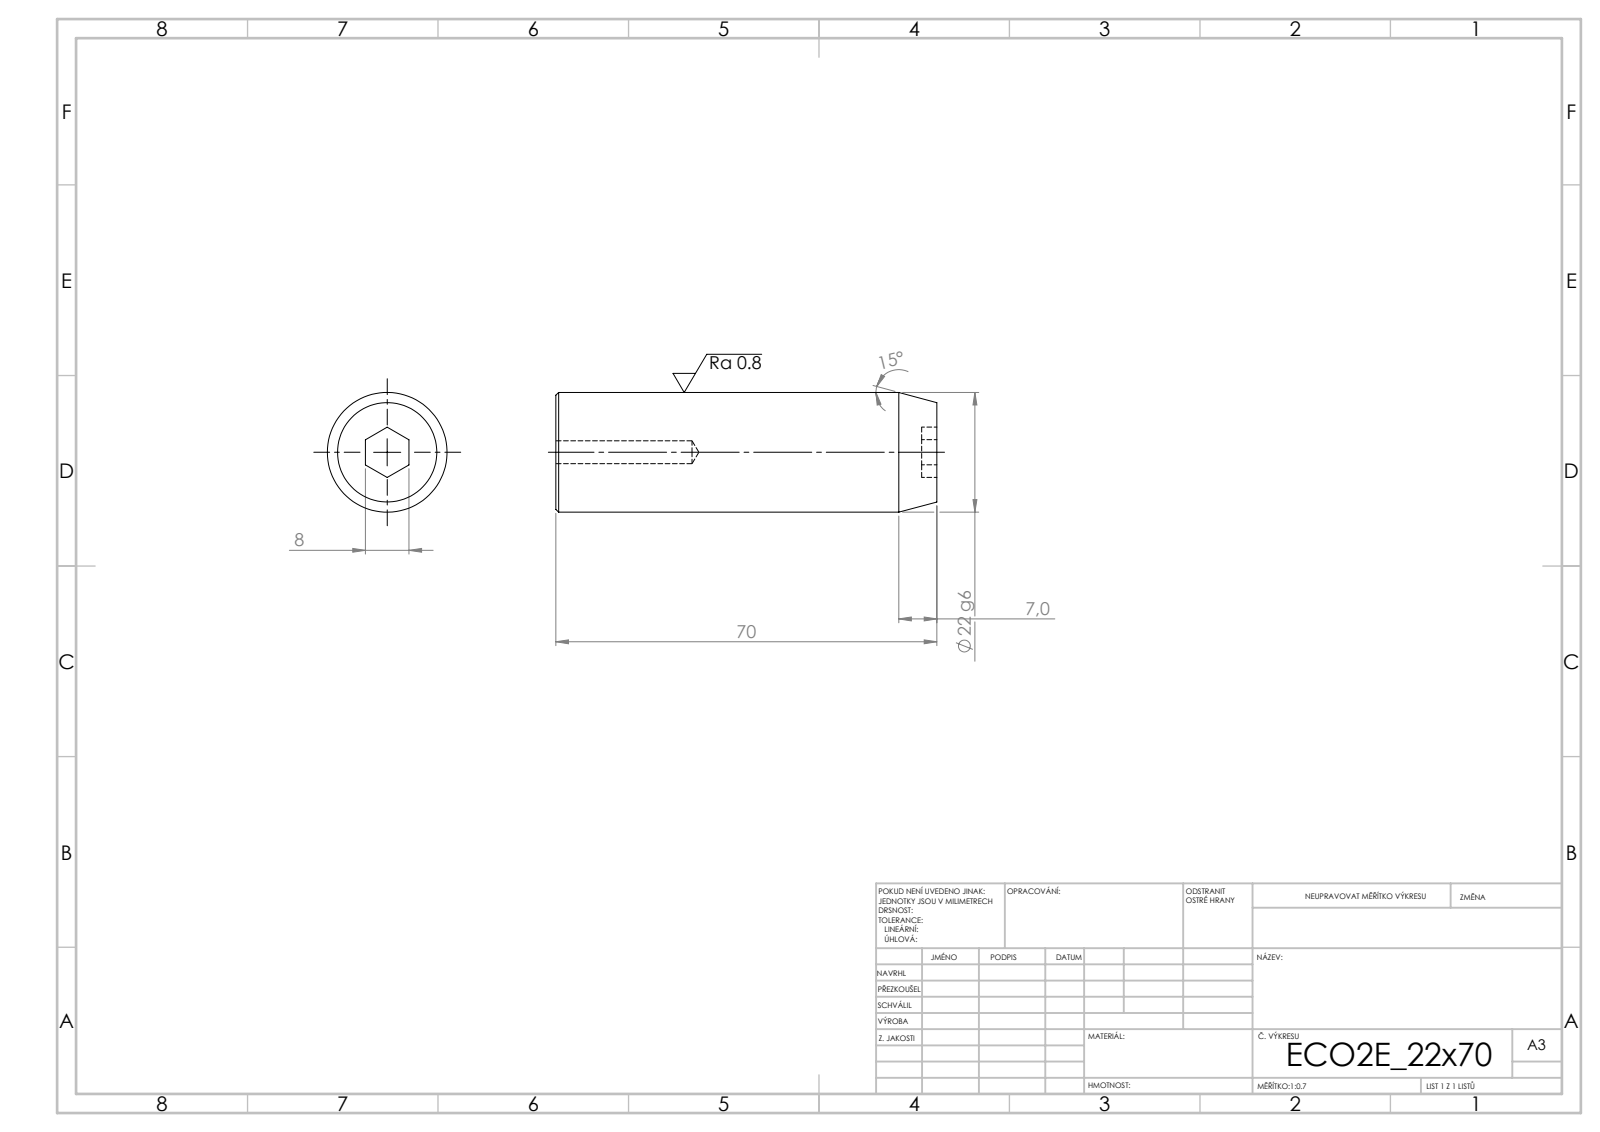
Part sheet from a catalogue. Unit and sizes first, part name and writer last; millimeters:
Units: millimetres
Overall size (bounding box): 70 × 22 × 22
Round holes (diameter × count): ⌀4.2 ×1
Round bosses / shafts (diameter × count): ⌀22 ×1
Main face-to-face distances: 70, 2.8, 67.2, 8
Volume: 25 665 mm³ · Surface area: 5 843 mm²
Bodies: 1 solid, 19 faces (9 planar, 4 cylindrical, 6 other)
STEP written by: SolidWorks 2019 (CONFIG_CONTROL_DESIGN)
